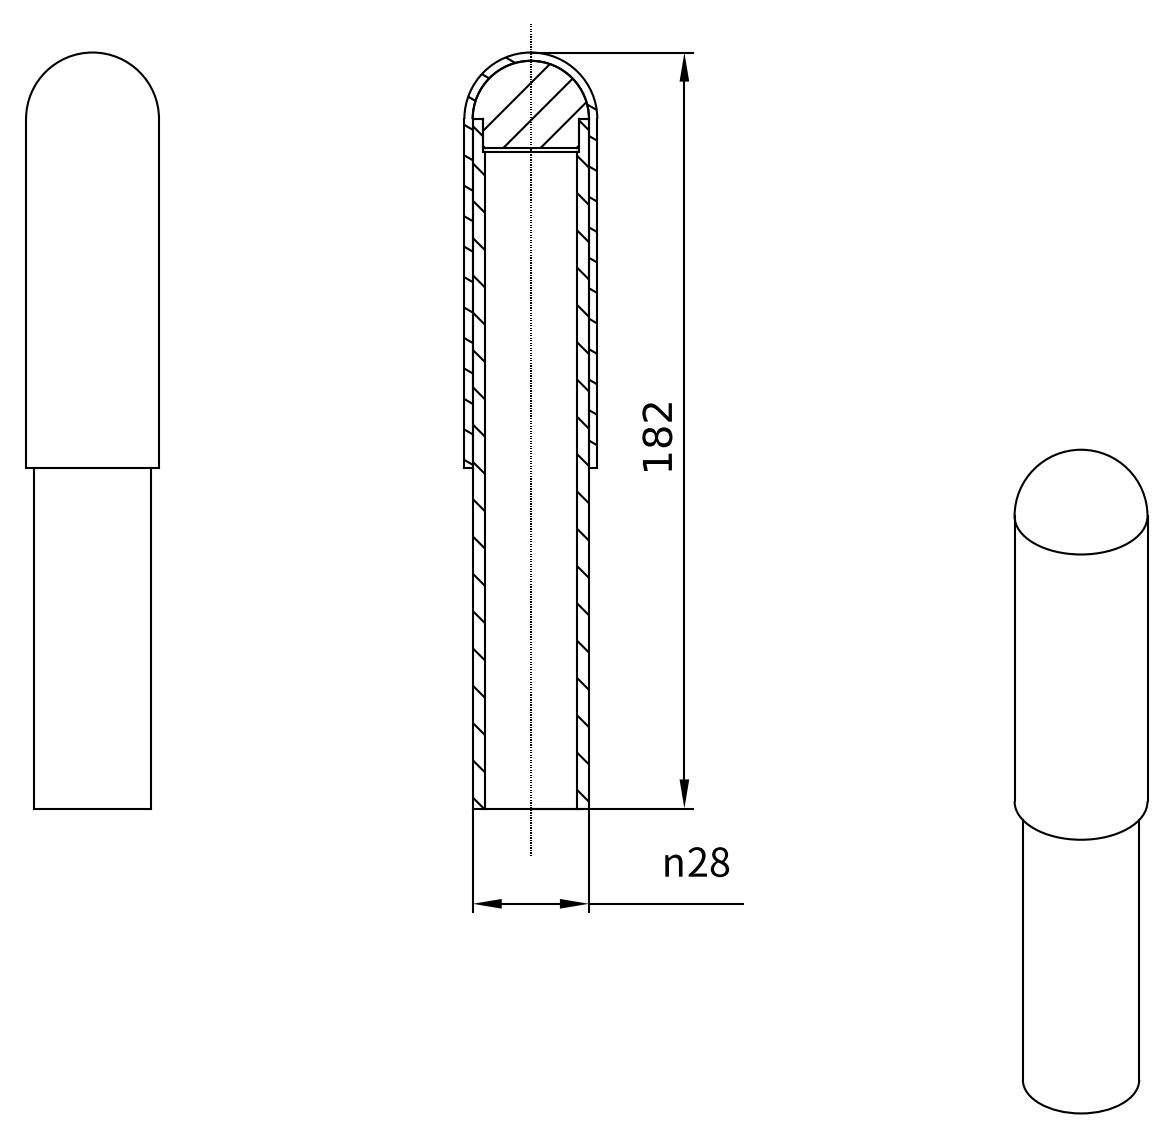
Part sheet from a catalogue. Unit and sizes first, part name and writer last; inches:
Units: inches
Overall size (bounding box): 7.165 × 1.26 × 1.26
Round holes (diameter × count): ⌀0.866 ×1, ⌀0.906 ×1
Round bosses / shafts (diameter × count): ⌀1.26 ×1, ⌀1.102 ×1
Main face-to-face distances: 6.26, 3.228, 3.031, 6.22, 2.992, 0.039
Volume: 4.036 in³ · Surface area: 45.24 in²
Bodies: 1 solid, 16 faces (4 planar, 8 cylindrical, 4 other)
STEP written by: Autodesk Inventor 8 (AUTOMOTIVE_DESIGN)
